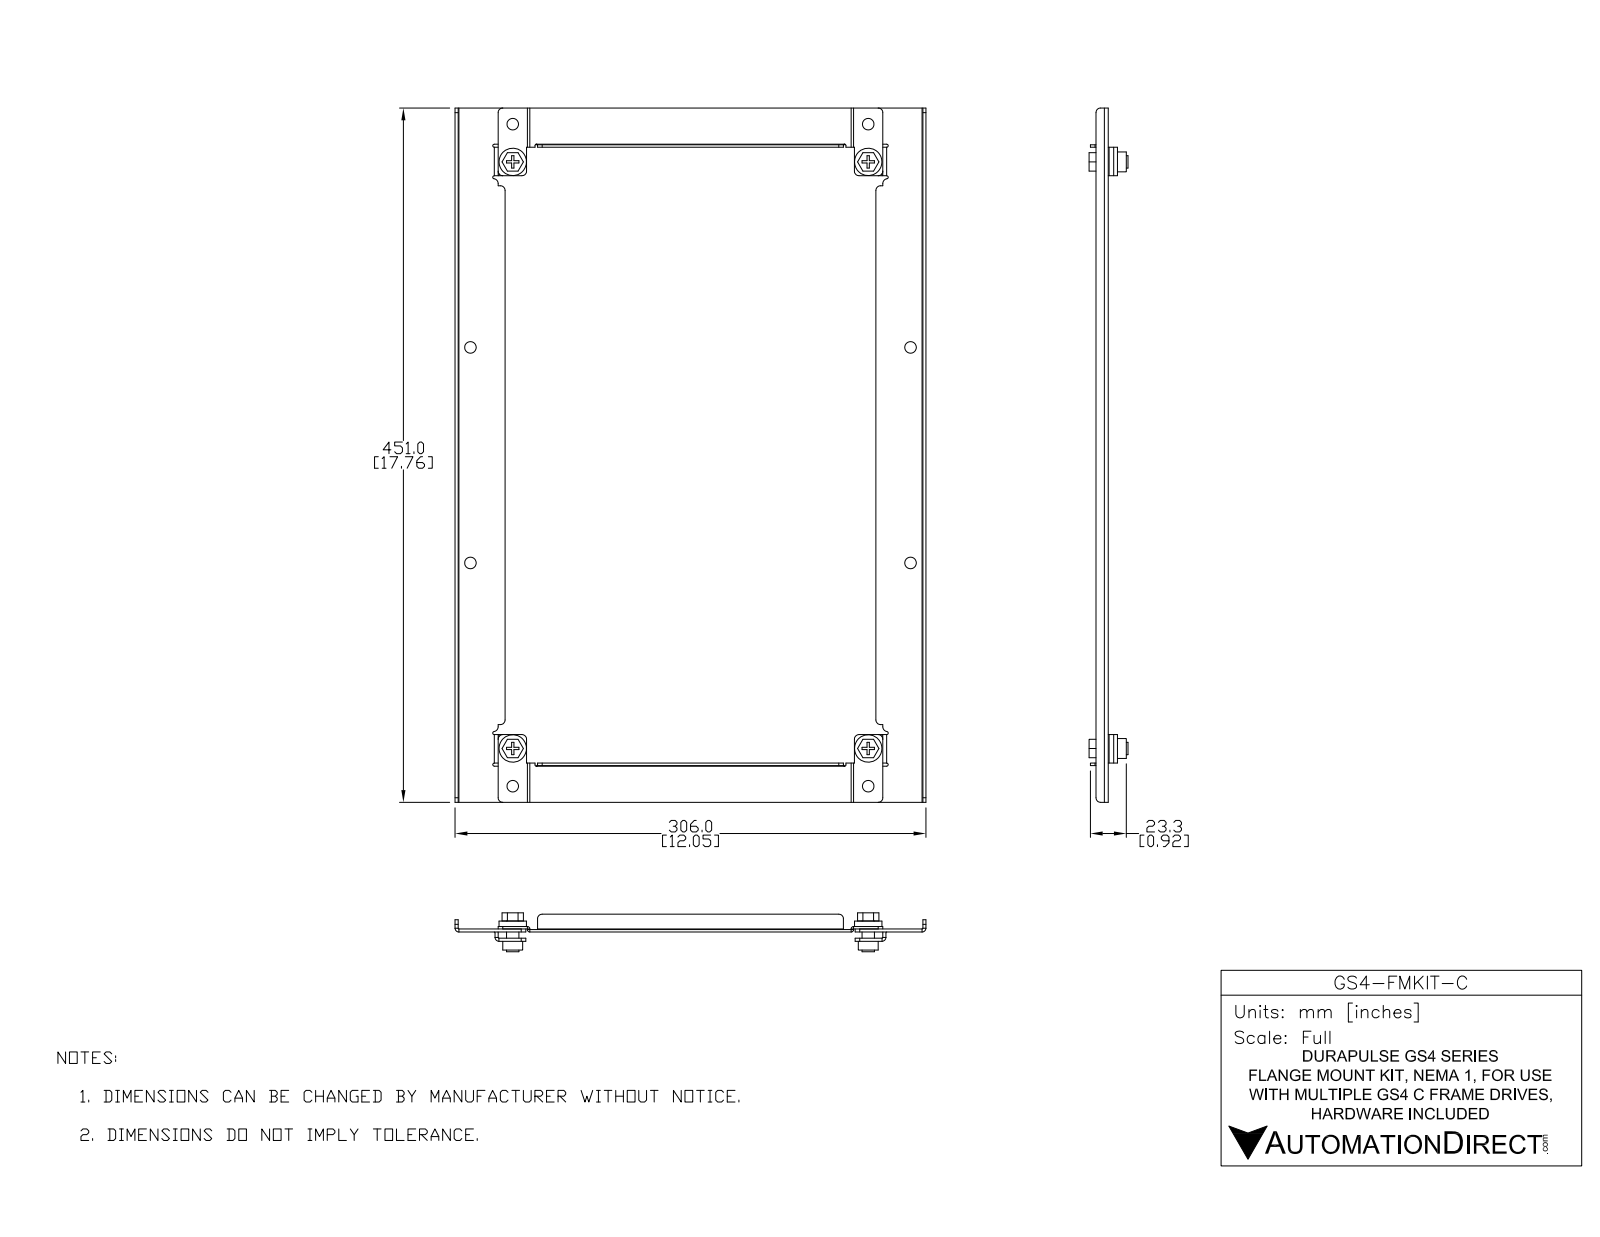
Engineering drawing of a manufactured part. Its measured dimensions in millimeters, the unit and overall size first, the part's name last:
Units: millimetres
Overall size (bounding box): 451 × 306 × 25.3
Round holes (diameter × count): ⌀7.5 ×4, ⌀17.8 ×4, ⌀8 ×2
Round bosses / shafts (diameter × count): ⌀8 ×6, ⌀12.9 ×4, ⌀7.5 ×4
Partial cylindrical surfaces — rounded edges, fillets, slot ends (radius × count): R3 ×40, R1 ×8, R0.5 ×6, R2.5 ×6, R1.6 ×4, R0.4 ×2, R2 ×2
Main face-to-face distances: 2, 1.6, 0.4, 304, 401.6, 6, 3.6, 8, 306, 302
Hole centre spacings: 24.5, 231, 232.3, 405.5, 466.68, 123.6, 147.58, 261.95
Bodies: 0 solids, 308 faces (148 planar, 132 cylindrical, 28 other)
Part name (STEP PRODUCT): GS4-FMKIT-C
STEP written by: SolidWorks 2015 (AUTOMOTIVE_DESIGN)
